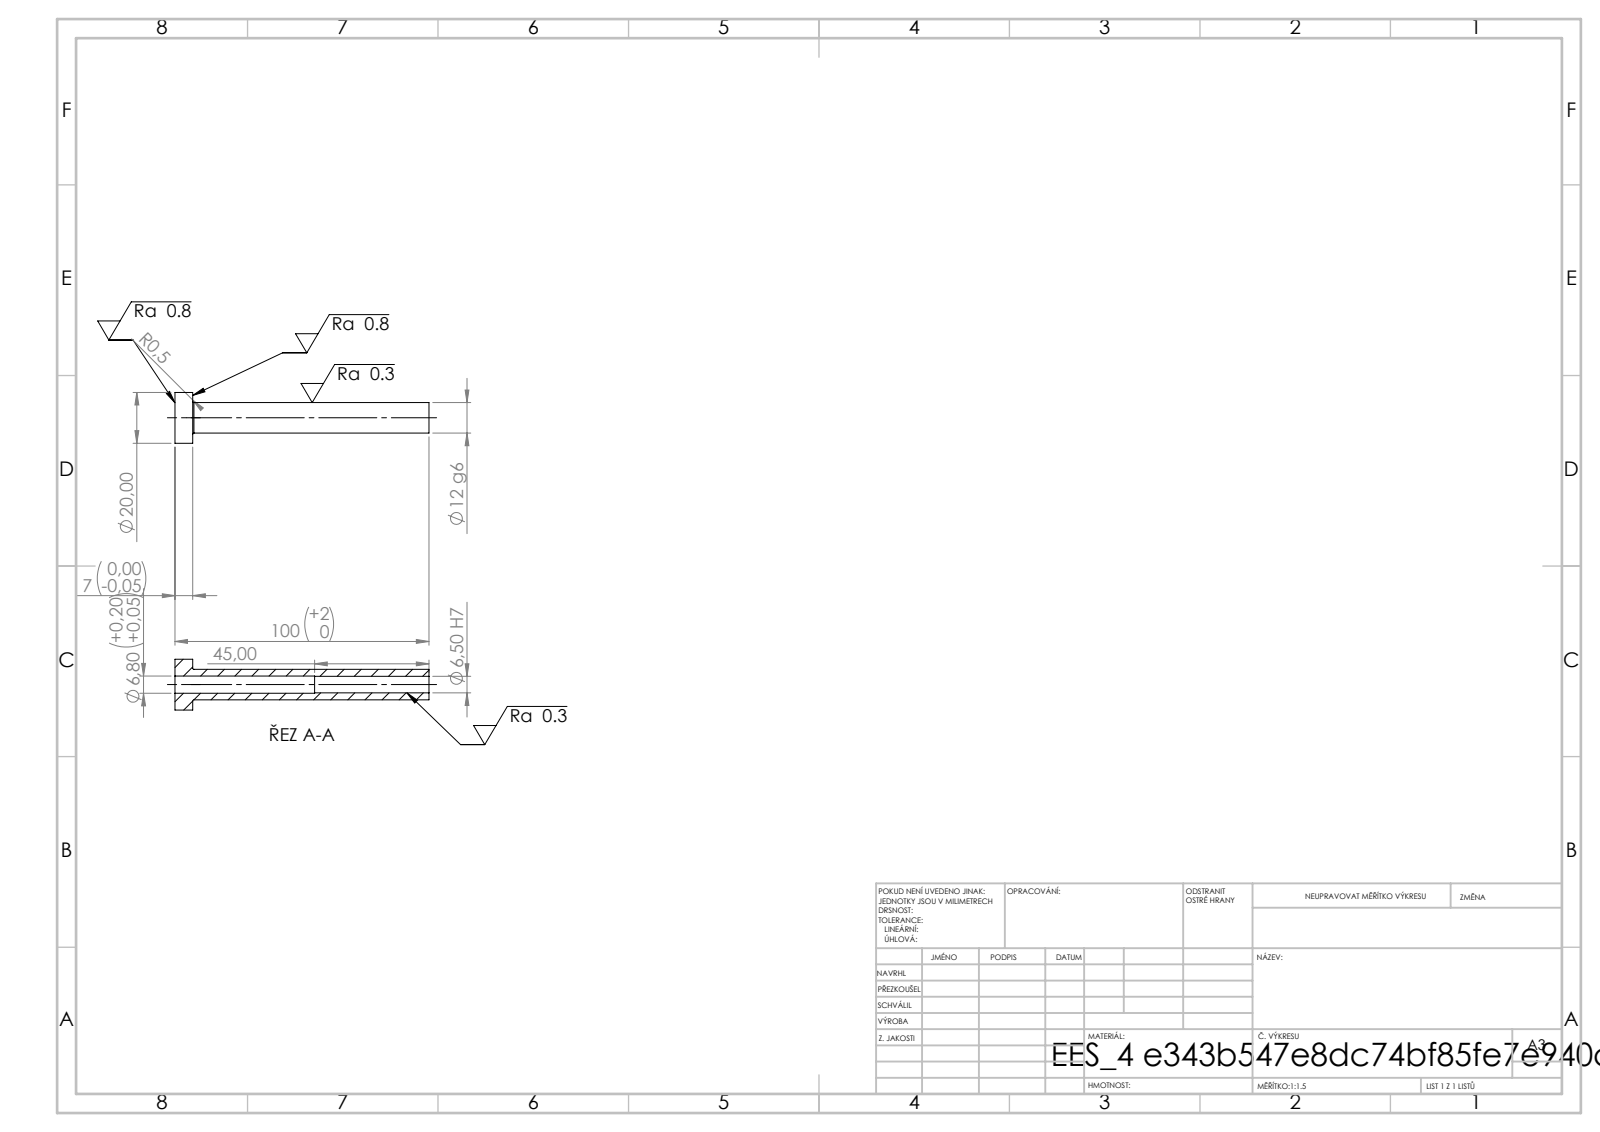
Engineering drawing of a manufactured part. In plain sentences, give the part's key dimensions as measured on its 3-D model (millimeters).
Its 3-D file was written by "SolidWorks 2019 (CONFIG_CONTROL_DESIGN)". It is 1 solid with 14 faces: 4 planar, 8 cylindrical and 2 other. Overall it measures 100 by 20 by 20 millimeters. Its volume is 9 229 cubic millimeters and its surface area 6 594 square millimeters. Round holes: 1 of diameter 6.5, 1 of diameter 6.8. Round bosses or shafts: 1 of diameter 20, 1 of diameter 12. The main face-to-face distances are 7, 100, 93, 55, 48, 45.
